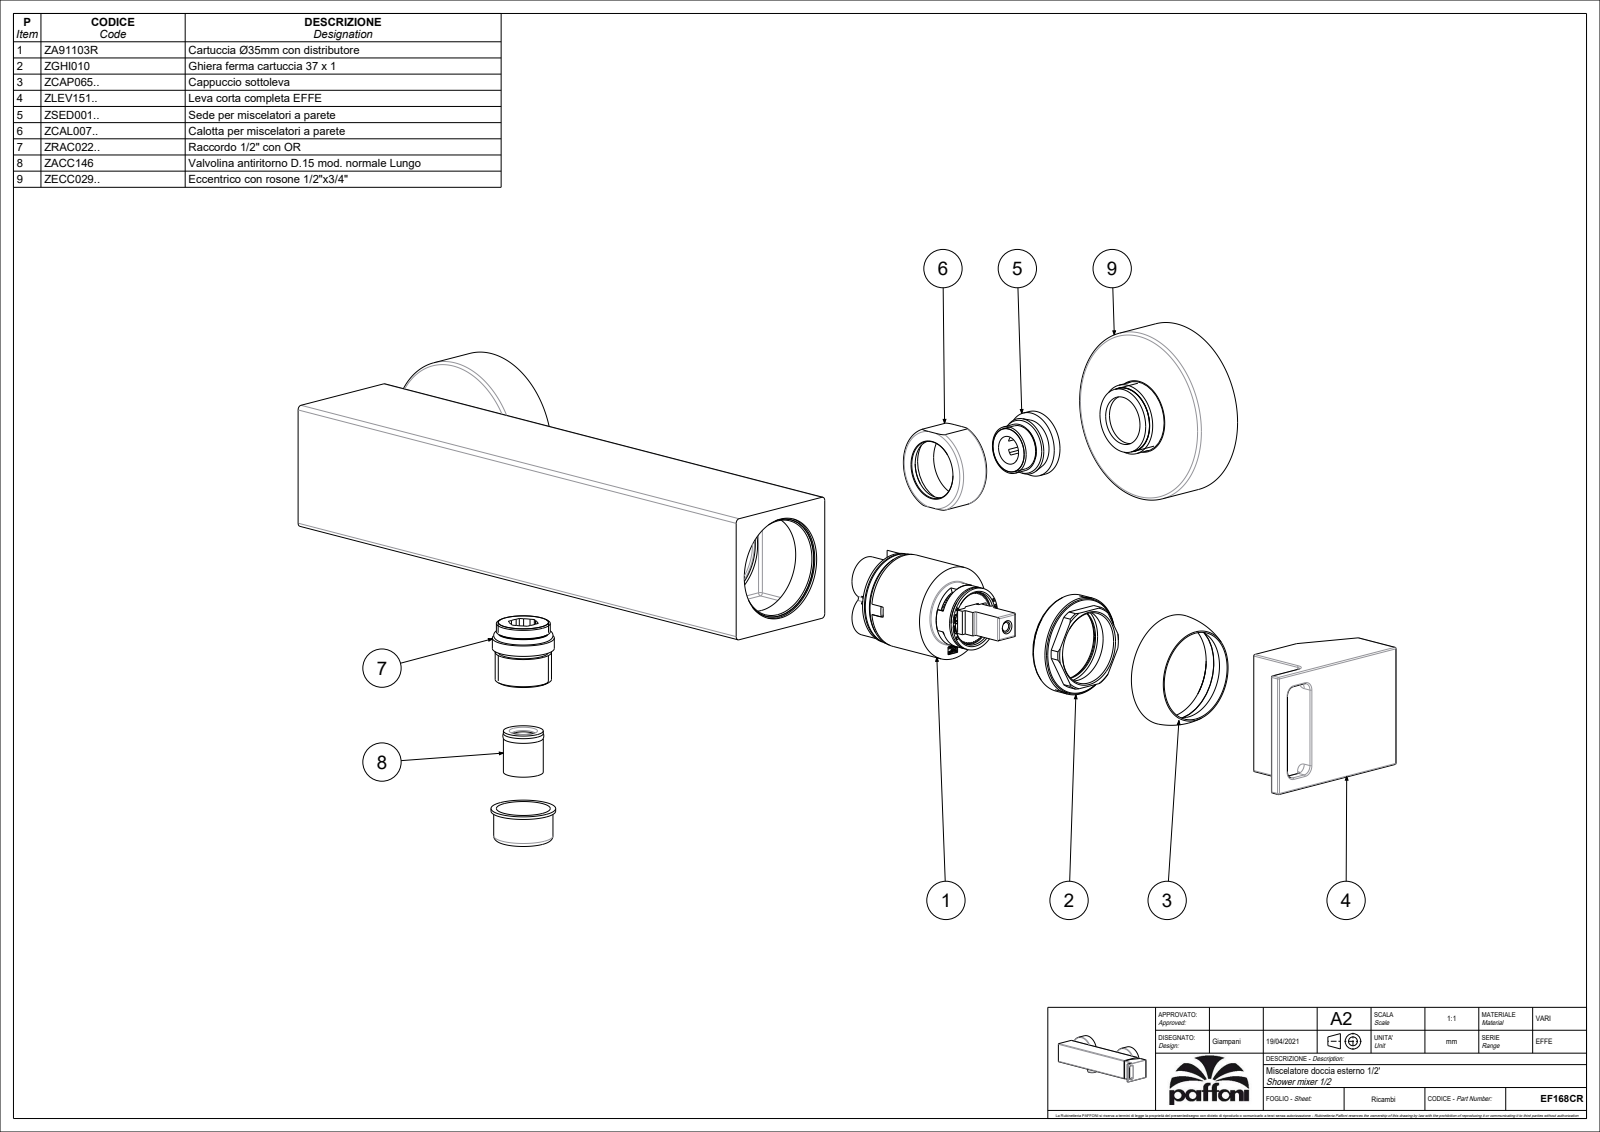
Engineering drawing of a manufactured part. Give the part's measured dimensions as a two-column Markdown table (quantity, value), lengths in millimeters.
| quantity | value |
| --- | --- |
| part name | EF168CR |
| STEP written by | CREO PARAMETRIC BY PTC INC, 2020044 (CONFIG_CONTROL_DESIGN) |
| units | millimeters |
| bodies | 1 solid, 1528 faces (736 planar, 460 cylindrical, 332 other) |
| overall size | 272.75 × 97.75 × 65.5 |
| volume | 263 838 mm³ |
| surface area | 170 914 mm² |
| round holes (diameter × count) | 9 × 3, 12 × 3, 4 × 2, 7 × 2, 8 × 2, 9.5 × 2, 10.5 × 2, 18 × 2, 20 × 2, 21.6 × 2, 37 × 2, 62.3 × 2 |
| round bosses / shafts (diameter × count) | 63.5 × 2, 27 × 2, 26.2 × 2, 20.5 × 2, 17.7 × 2, 35 × 1, 34.8 × 1, 33.8 × 1 |
| partial cylindrical surfaces (radius × count) | 1 × 90, 0.5 × 60, 0.15 × 11, 0.3 × 9, 3 × 6, 1.5 × 4, 6 × 4, 7 × 4 |
| main face-to-face distances | 3.75, 42.75, 46.5, 39, 3, 15, 42, 18.75, 57.75, 61.5 |
| hole center spacings | 0.71, 8.51, 8.6, 13.04, 13.21, 13.51, 6, 9.5 |
